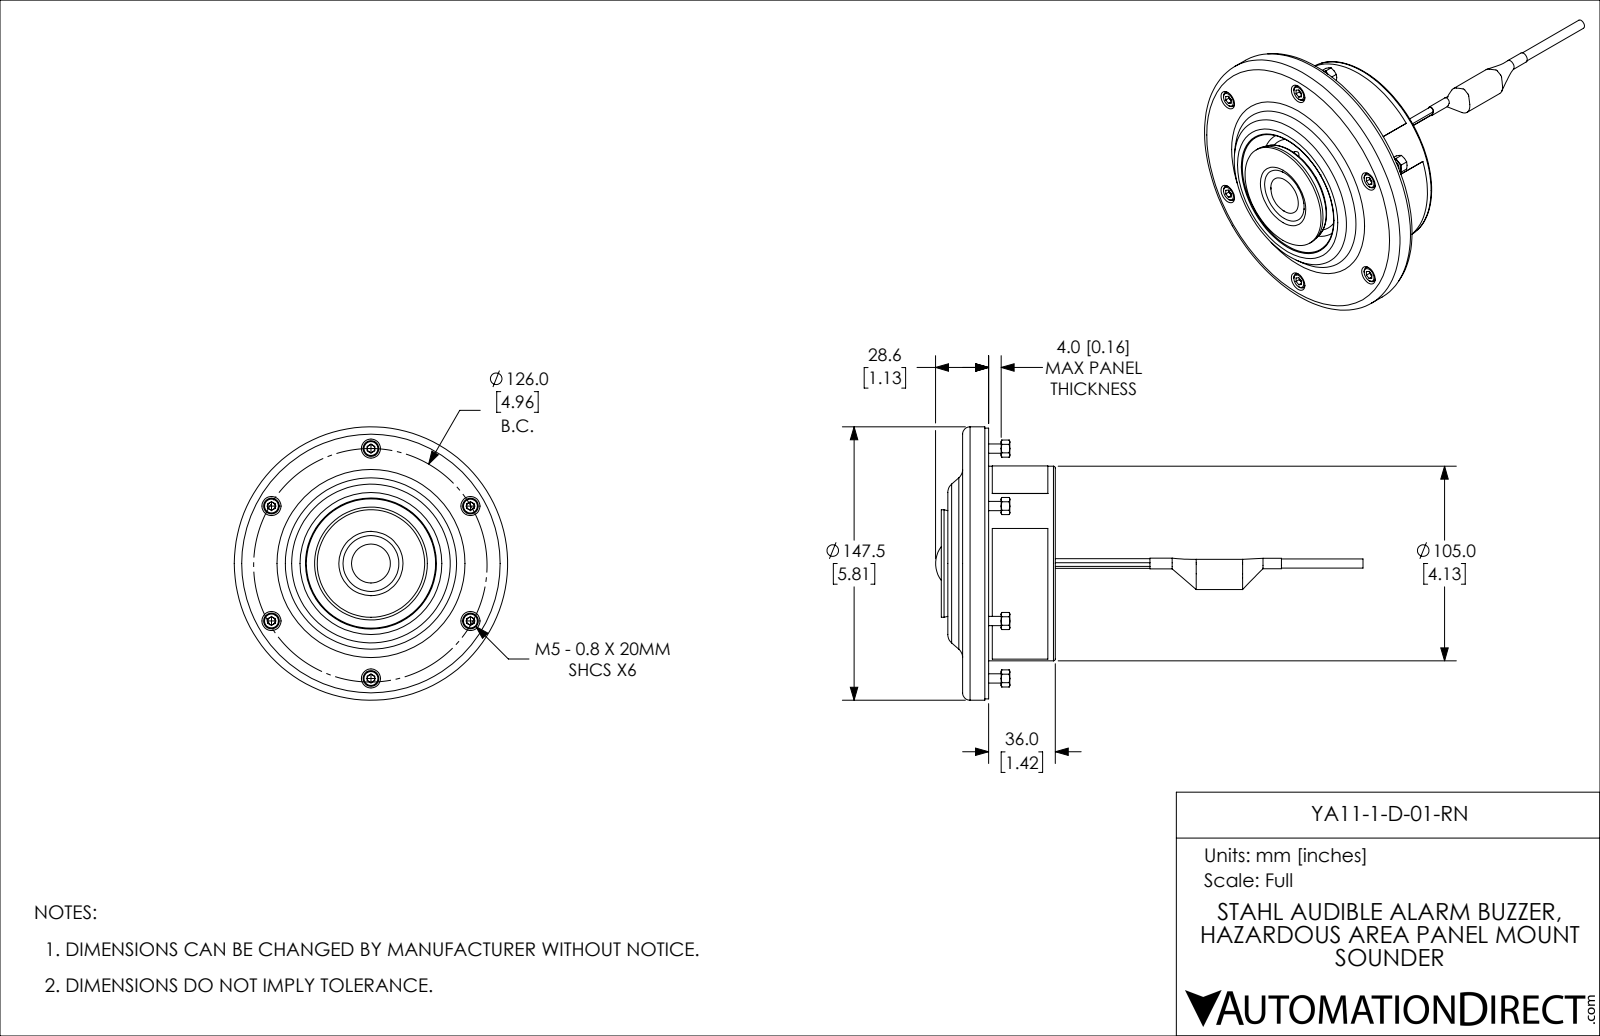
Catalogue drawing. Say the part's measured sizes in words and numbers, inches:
The part is named "YA11-1-D-01-RN". Its 3-D file was written by "SolidWorks 2019 (CONFIG_CONTROL_DESIGN)". It is 23 solids with 589 faces: 207 planar, 168 cylindrical and 214 other. Overall it measures 5.807 by 5.807 by 5.028 inches. Its volume is 20.75 cubic inches and its surface area 219.4 square inches. Round holes: 6 of diameter 0.165, 6 of diameter 0.197, 6 of diameter 0.209, 6 of diameter 0.217, 6 of diameter 0.406, 3 of diameter 0.157, 3 of diameter 0.256, 2 of diameter 0.098, 1 of diameter 0.276, 1 of diameter 0.374, 1 of diameter 0.394, 1 of diameter 1.85. Round bosses or shafts: 6 of diameter 0.335, 1 of diameter 5.807, 1 of diameter 5.748, 1 of diameter 3.819, 1 of diameter 3.724, 1 of diameter 2.283, 1 of diameter 0.512. Partial cylindrical surfaces (rounded edges, fillets, slot ends): 4 of radius 0.079, 2 of radius 0.039, 2 of radius 0.051, 2 of radius 0.063, 1 of radius 2.071, 1 of radius 2.075. The main face-to-face distances are 1.24, 0.079, 1.161, 1.181, 0.059, 1.102, 0.472, 1.713, 1.654, 0.551. The hole center spacings are 2.441, 2.153, 2.12, 2.933, 3.112, 4.228, 0.813, 1.628.
